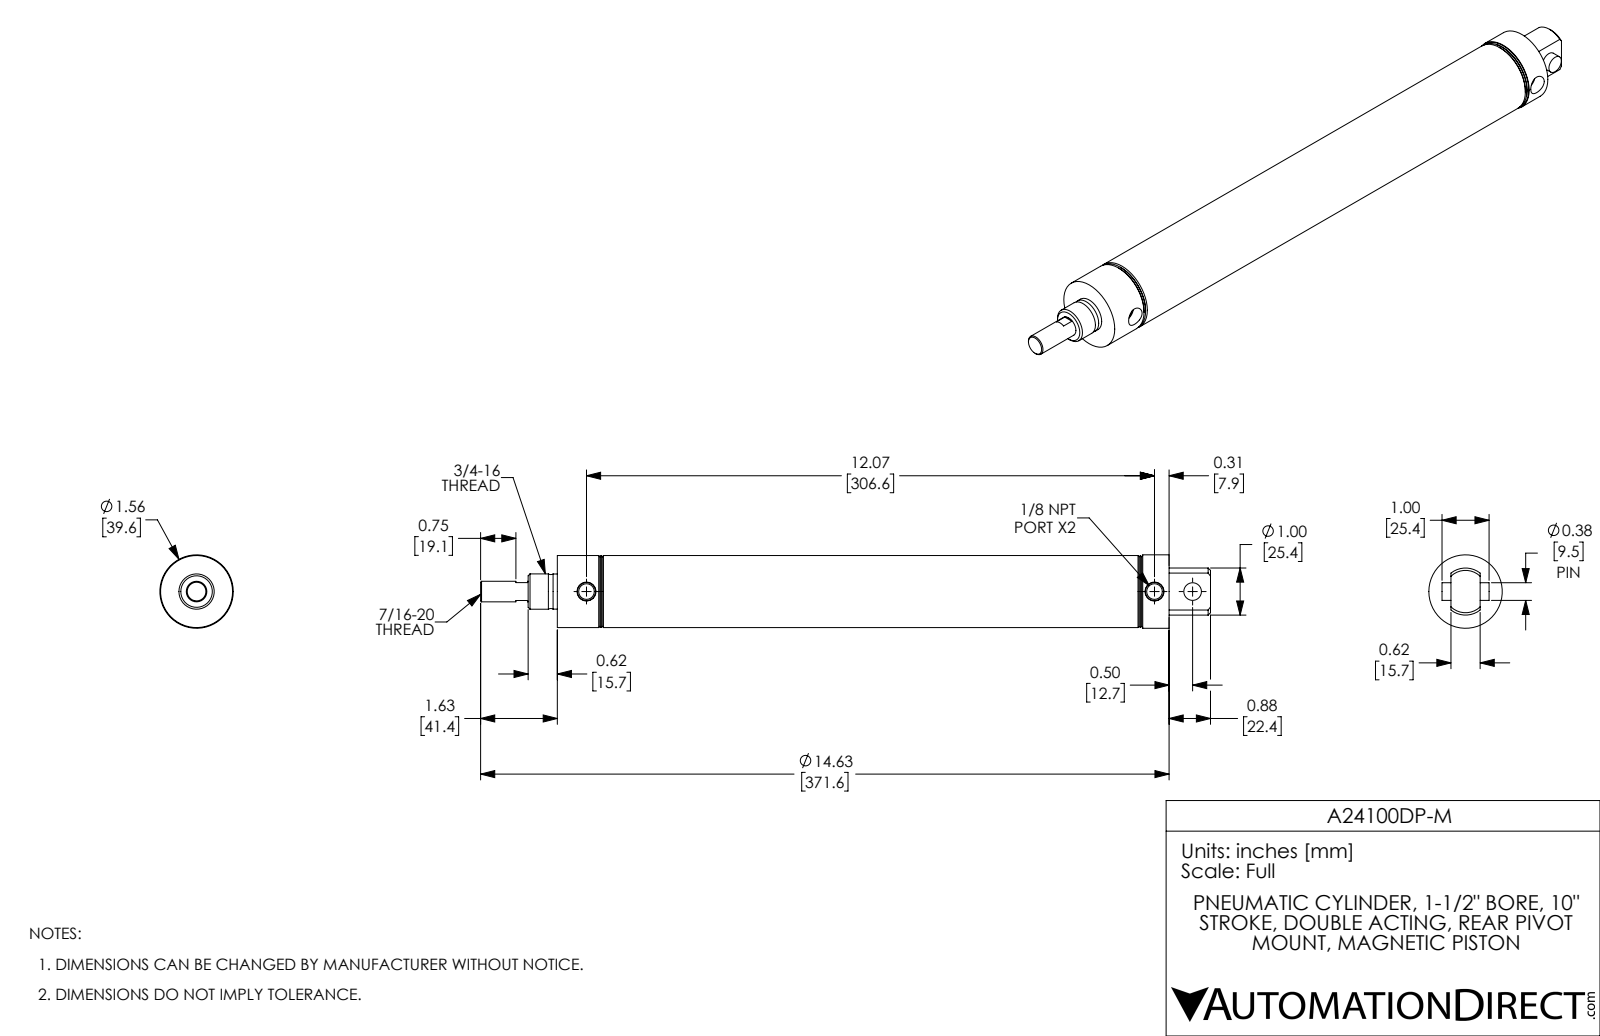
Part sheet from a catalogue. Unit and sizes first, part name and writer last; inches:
Units: inches
Overall size (bounding box): 15.51 × 1.56 × 1.56
Round holes (diameter × count): ⌀0.332 ×2, ⌀0.375 ×1, ⌀0.437 ×1, ⌀1.5 ×1
Round bosses / shafts (diameter × count): ⌀1.56 ×1, ⌀1.53 ×1, ⌀0.75 ×1, ⌀0.746 ×1
Partial cylindrical surfaces — rounded edges, fillets, slot ends (radius × count): R0.5 ×1
Main face-to-face distances: 1.25, 11.75, 10.5, 0.5, 10, 11.25, 1.75, 13, 0.62, 0.88
Hole centre spacings: 0.81, 12.07, 12.88
Volume: 8.623 in³ · Surface area: 152.4 in²
Bodies: 3 solids, 84 faces (22 planar, 28 cylindrical, 34 other)
Part name (STEP PRODUCT): A24100DP-M-MainBody; A24100DP-M-Rod; A24100DP-M-Pin; A24100DP-M
STEP written by: SolidWorks 2017 (AUTOMOTIVE_DESIGN)
